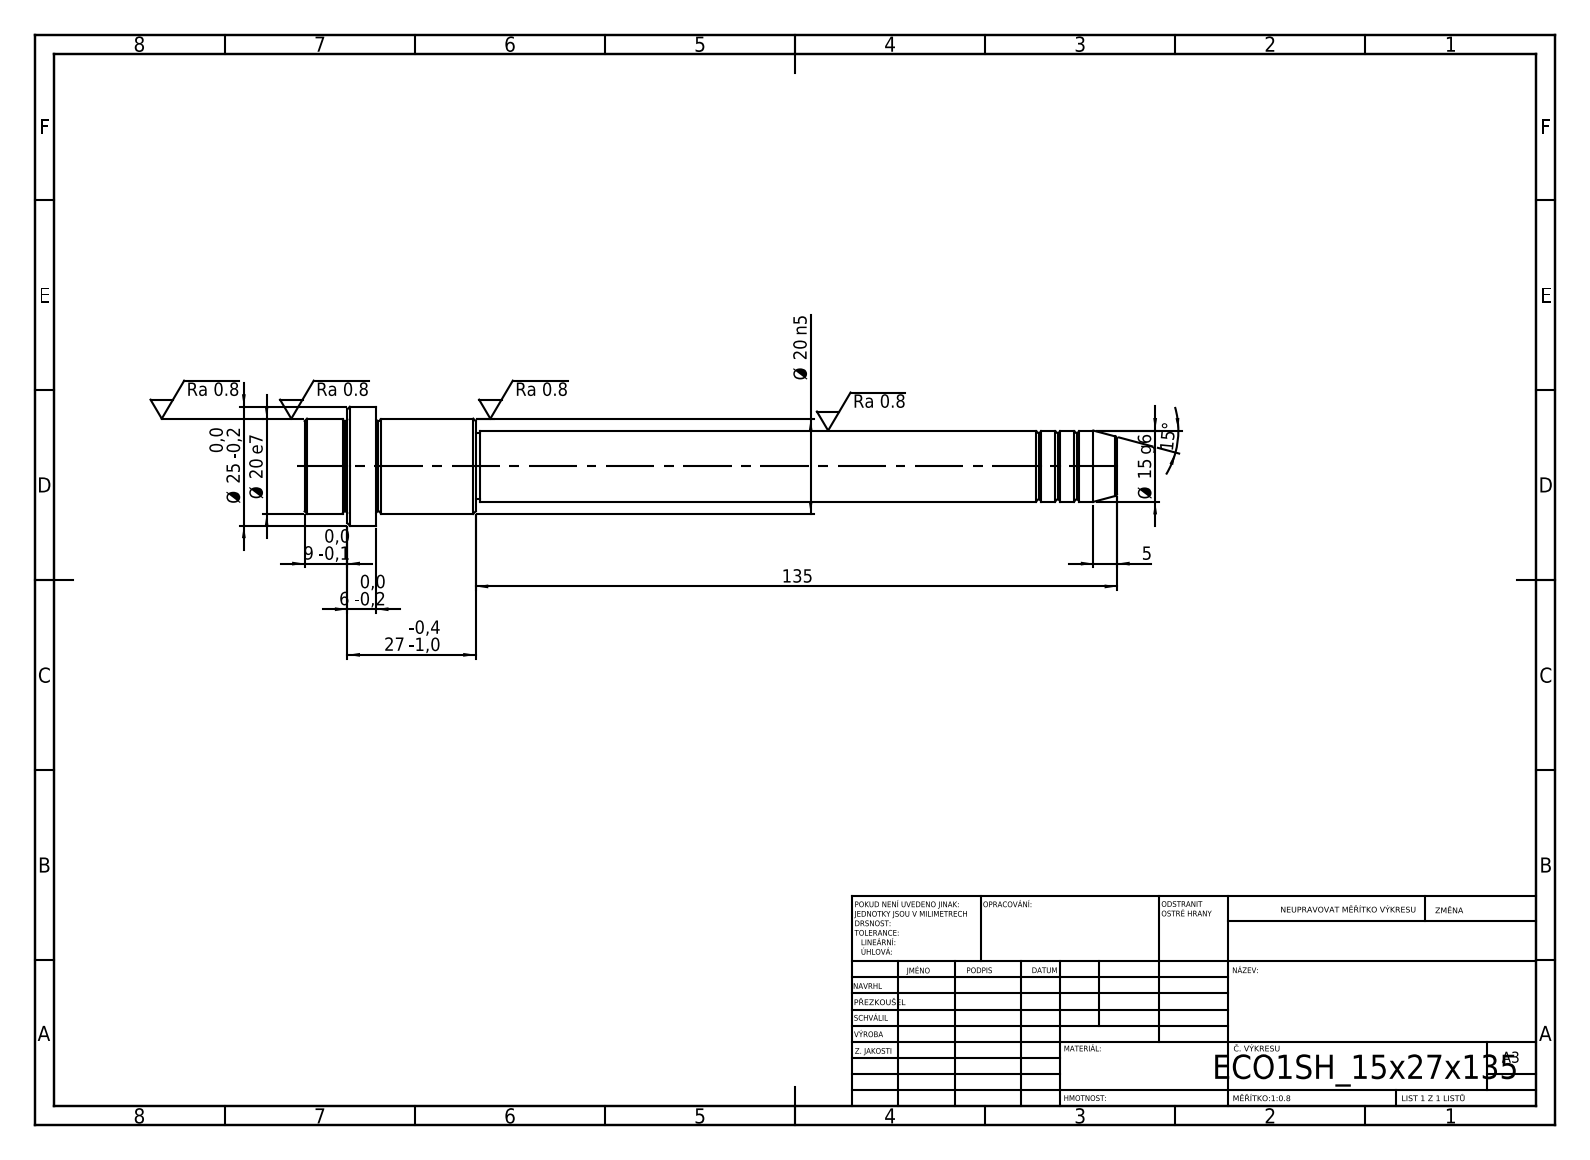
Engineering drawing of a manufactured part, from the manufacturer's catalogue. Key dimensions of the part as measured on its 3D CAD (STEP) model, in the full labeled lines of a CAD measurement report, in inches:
STEP written by: SolidWorks 2019 (CONFIG_CONTROL_DESIGN)
Units: inches
Bodies: 1 solid, 52 faces (6 planar, 16 cylindrical, 30 other)
Overall size (bounding box): 6.732 × 0.984 × 0.984
Volume: 2.192 in³ · Surface area: 15.1 in²
Round bosses / shafts (diameter × count): ⌀0.984 ×1, ⌀0.787 ×1, ⌀0.591 ×1, ⌀0.551 ×1
Main face-to-face distances: 0.591, 0.236, 0.354, 0.827, 1.063, 1.417, 5.315, 6.142, 6.378, 6.732
